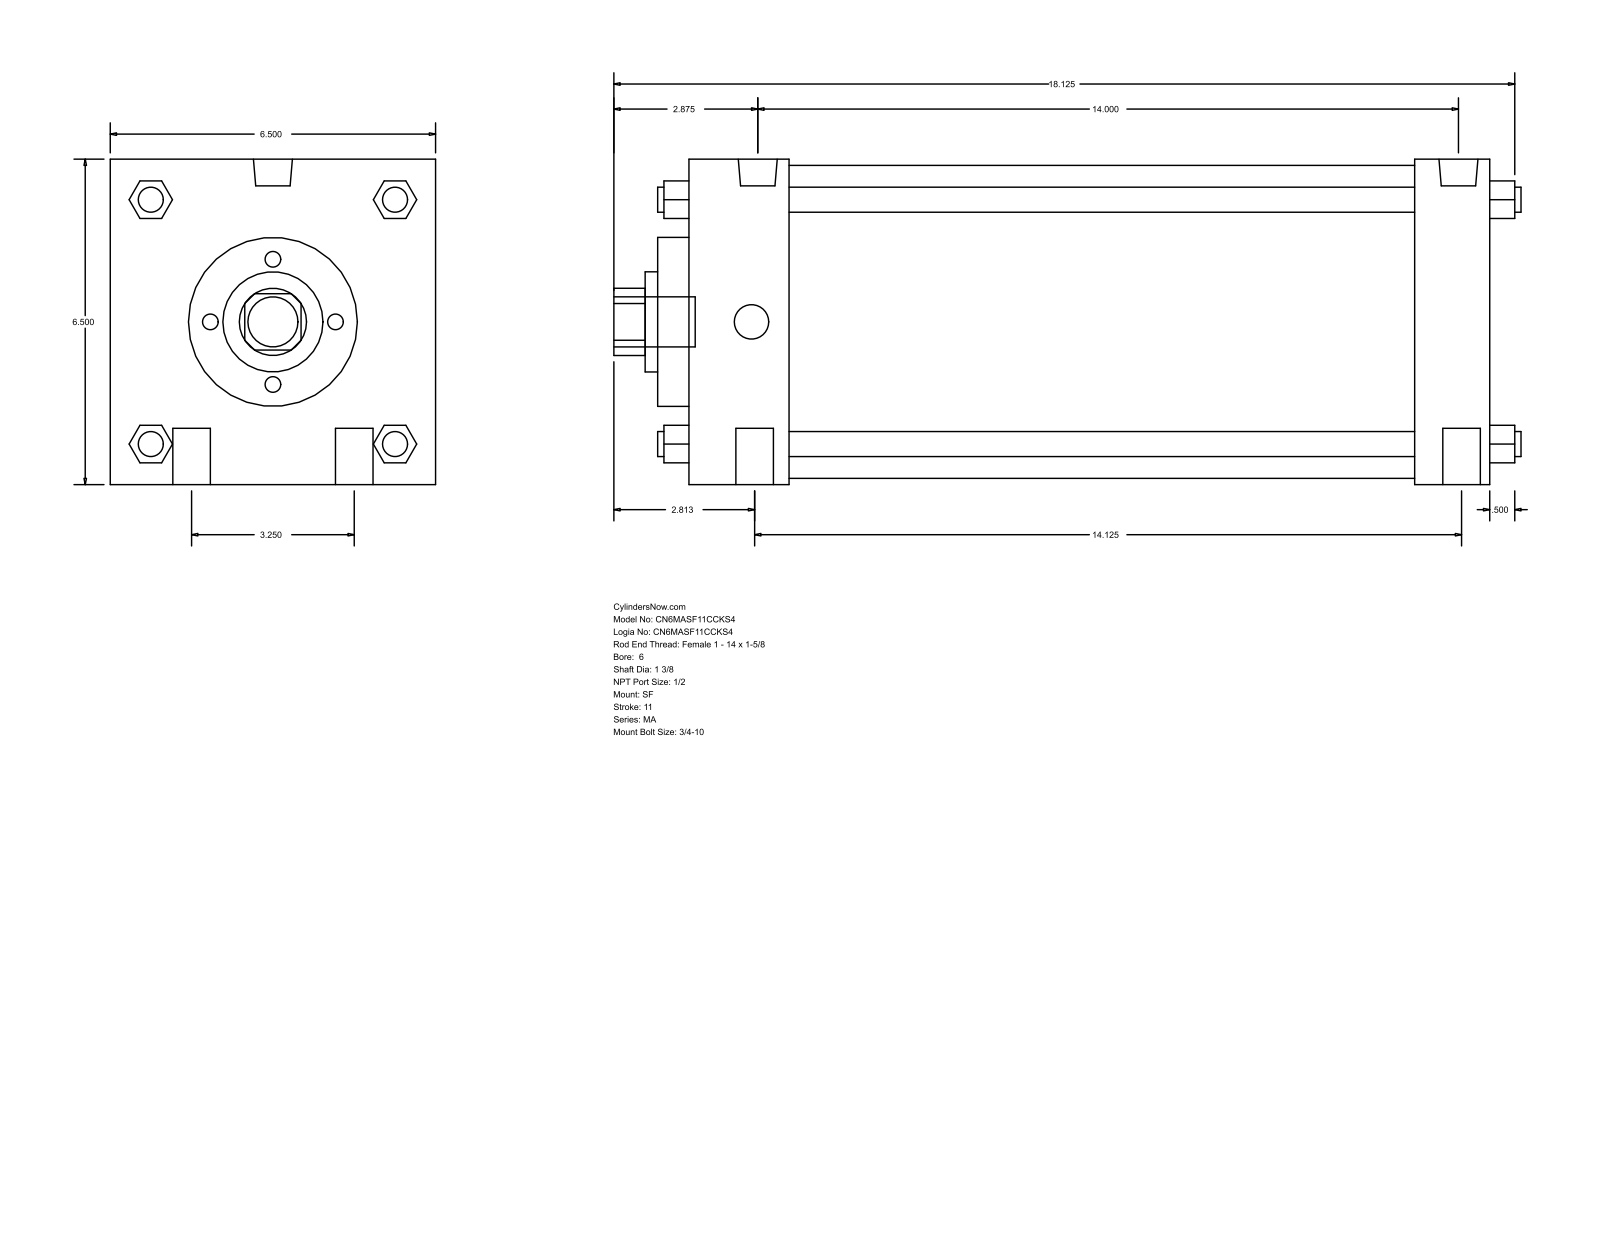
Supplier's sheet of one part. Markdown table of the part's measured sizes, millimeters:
| quantity | value |
| --- | --- |
| part name | MA_SF__0600_1.375 |
| STEP written by | GSSL Pune (CONFIG_CONTROL_DESIGN) |
| units | millimeters |
| bodies | 0 solids, 126 faces (95 planar, 31 cylindrical, 0 other) |
| overall size | 460.38 × 165.1 × 165.1 |
| round holes (diameter × count) | 34.92 × 1, 50.8 × 1, 85.72 × 1, 158.75 × 1 |
| round bosses / shafts (diameter × count) | 19.05 × 4, 12.7 × 4, 19.77 × 2, 17.46 × 2, 25.4 × 1 |
| partial cylindrical surfaces (radius × count) | 17.06 × 1 |
| main face-to-face distances | 165.1, 406.4, 368.3, 50.8, 38.1, 317.5, 355.6, 15.87, 66.67, 384.17 |
